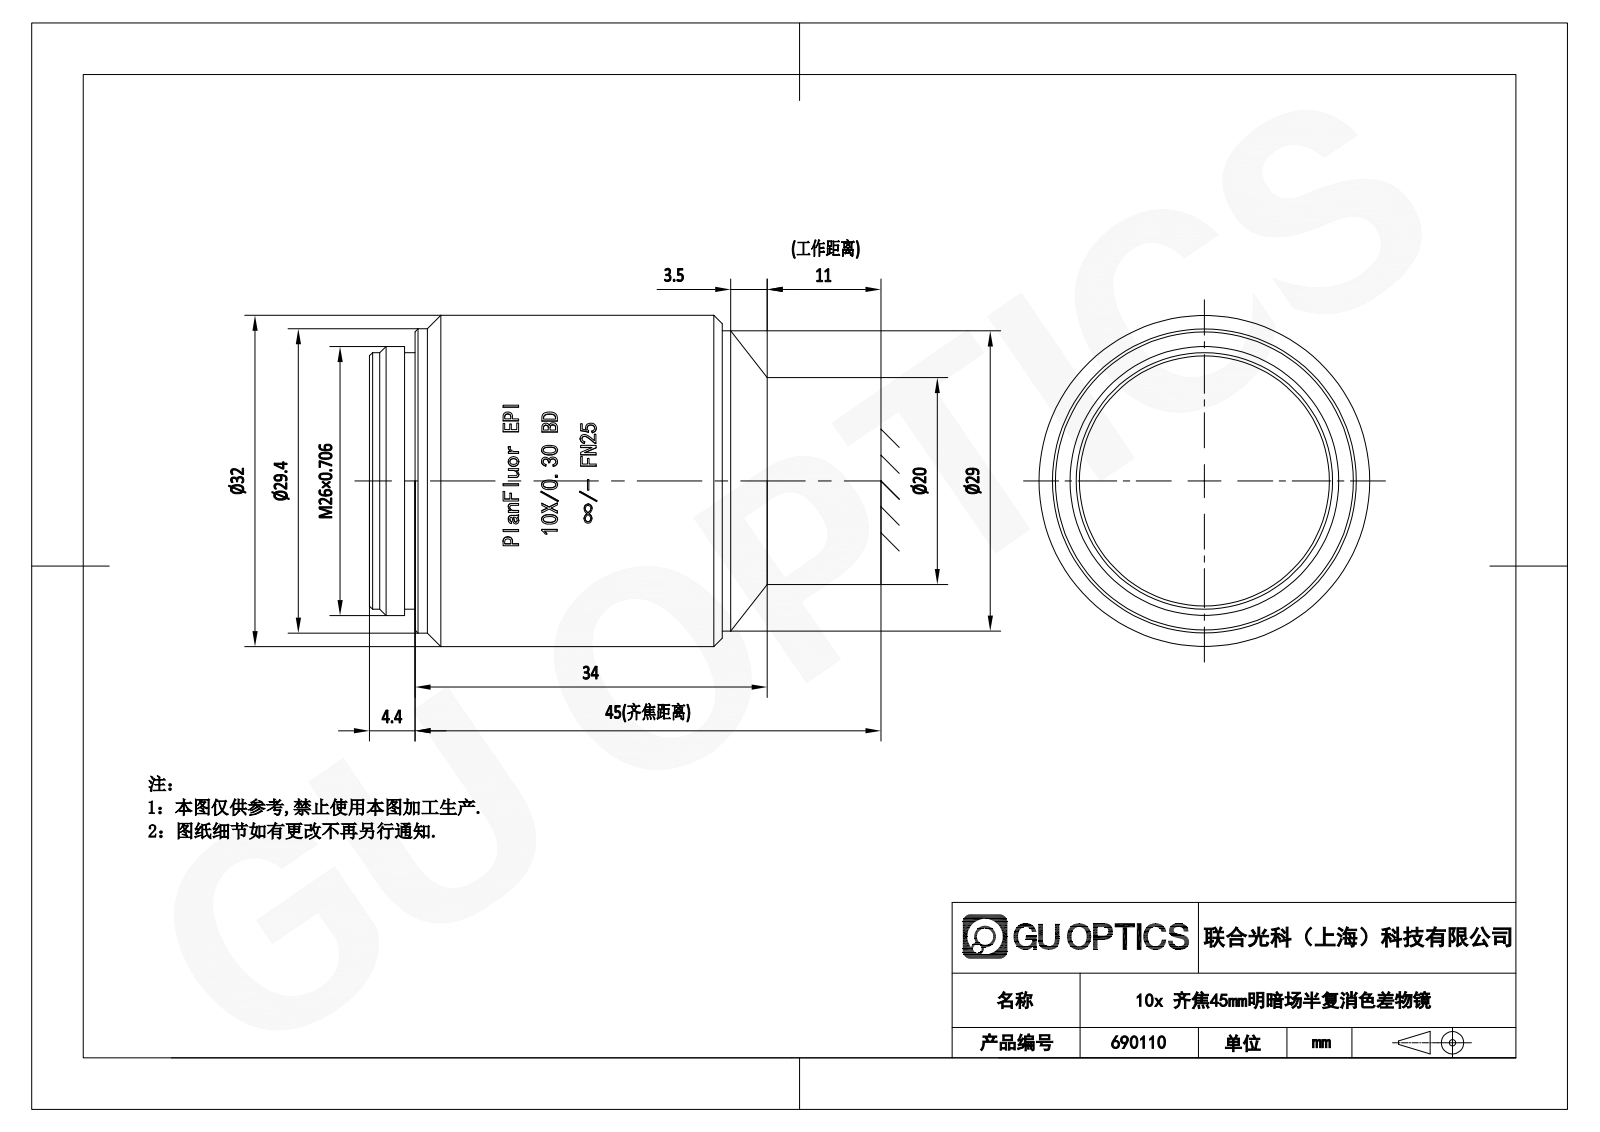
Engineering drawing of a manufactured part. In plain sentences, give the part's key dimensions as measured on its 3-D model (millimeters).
The part is named "690110". Its 3-D file was written by "SolidWorks 2020 (CONFIG_CONTROL_DESIGN)". It is 1 solid with 333 faces: 145 planar, 53 cylindrical and 135 other. Overall it measures 38.45 by 32.05 by 32 millimeters. Its volume is 28 066 cubic millimeters and its surface area 5 023 square millimeters. Round bosses or shafts: 1 of diameter 32, 1 of diameter 29.4, 1 of diameter 29, 1 of diameter 26, 1 of diameter 24.8. Partial cylindrical surfaces (rounded edges, fillets, slot ends): 1 of radius 16.05. The main face-to-face distances are 38.45, 4.4, 34.05, 34.1, 29.7, 4.35, 3.4, 1, 30.7, 35.05.
